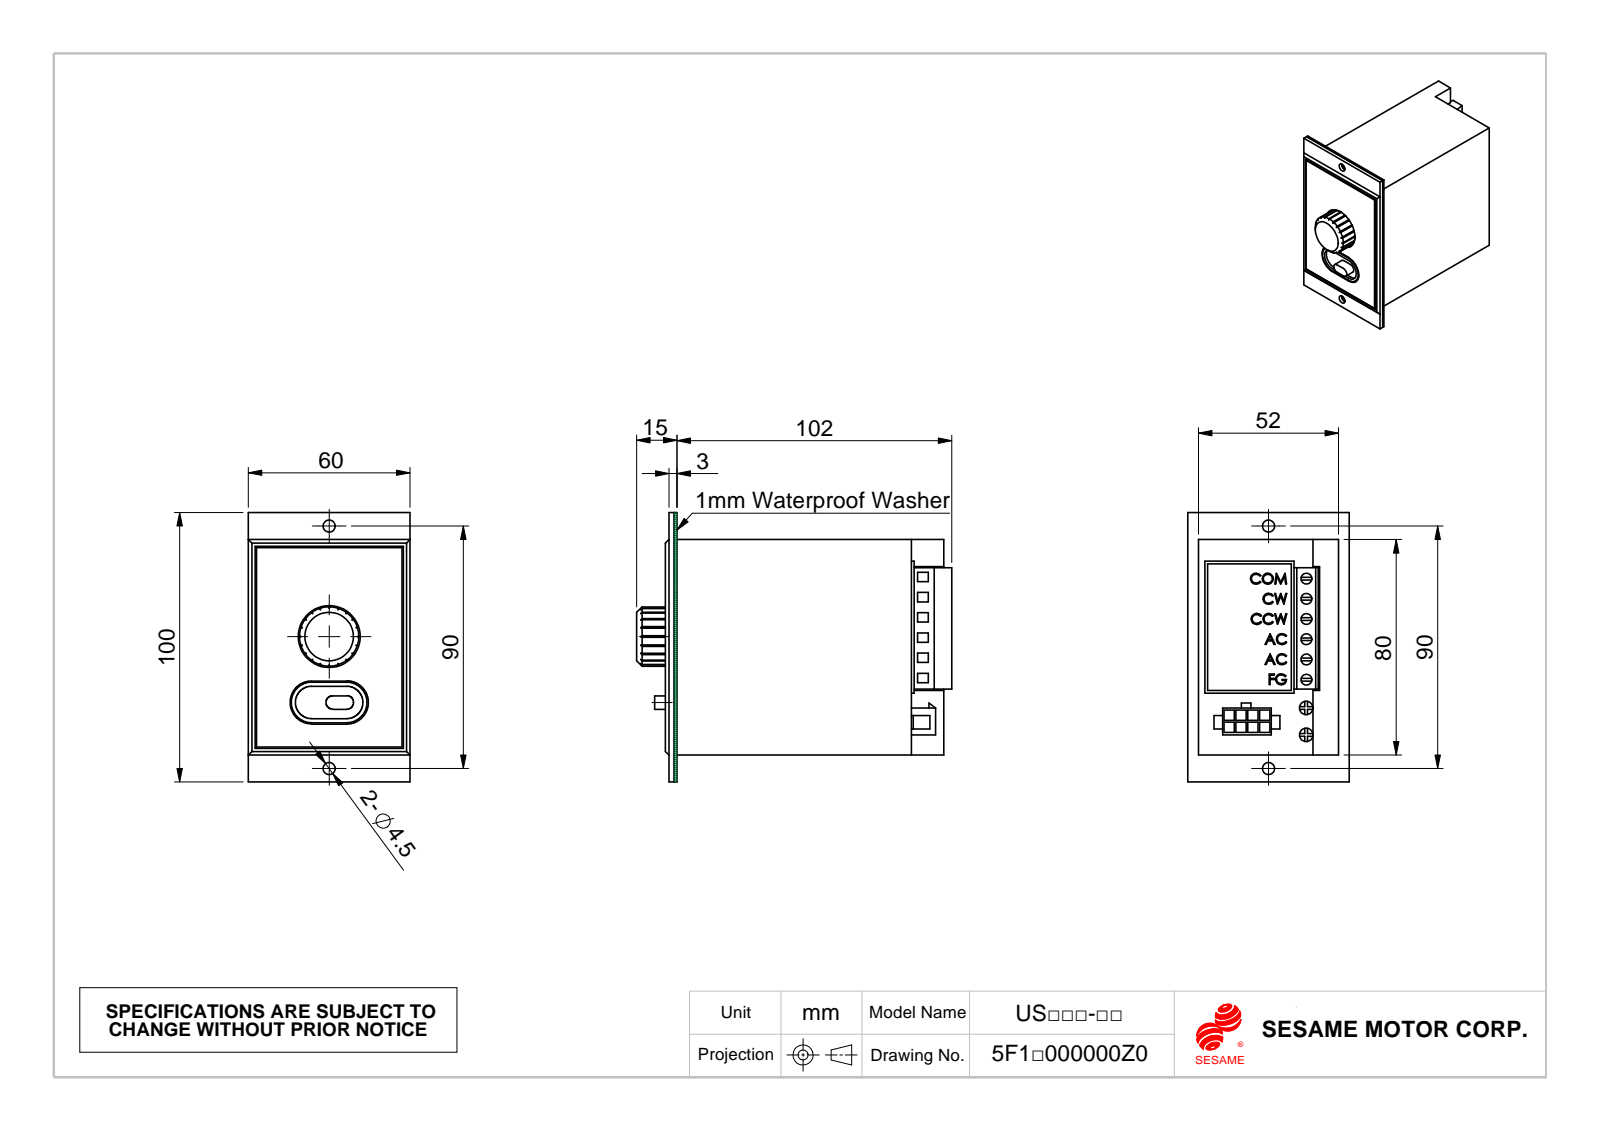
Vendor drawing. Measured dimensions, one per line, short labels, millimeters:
written by: SolidWorks 2010 (CONFIG_CONTROL_DESIGN)
unit: mm
bodies: 2 solids, 497 faces (384 planar, 40 cylindrical, 73 other)
size: 117 × 100 × 60
volume: 403 570 mm³; area: 47 761 mm²
holes: 6× ⌀4, 2× ⌀4.5, 2× ⌀5, 1× ⌀23
bosses: 1× ⌀22
rounds: 2× R2.5, 2× R6, 2× R7.5, 2× R8
face distances: 52, 80, 3.3, 88, 91.3, 1, 4.3, 87, 2, 90
hole spacings: 7.5, 15, 22.5, 30, 10, 10.5, 14.12, 15.51
